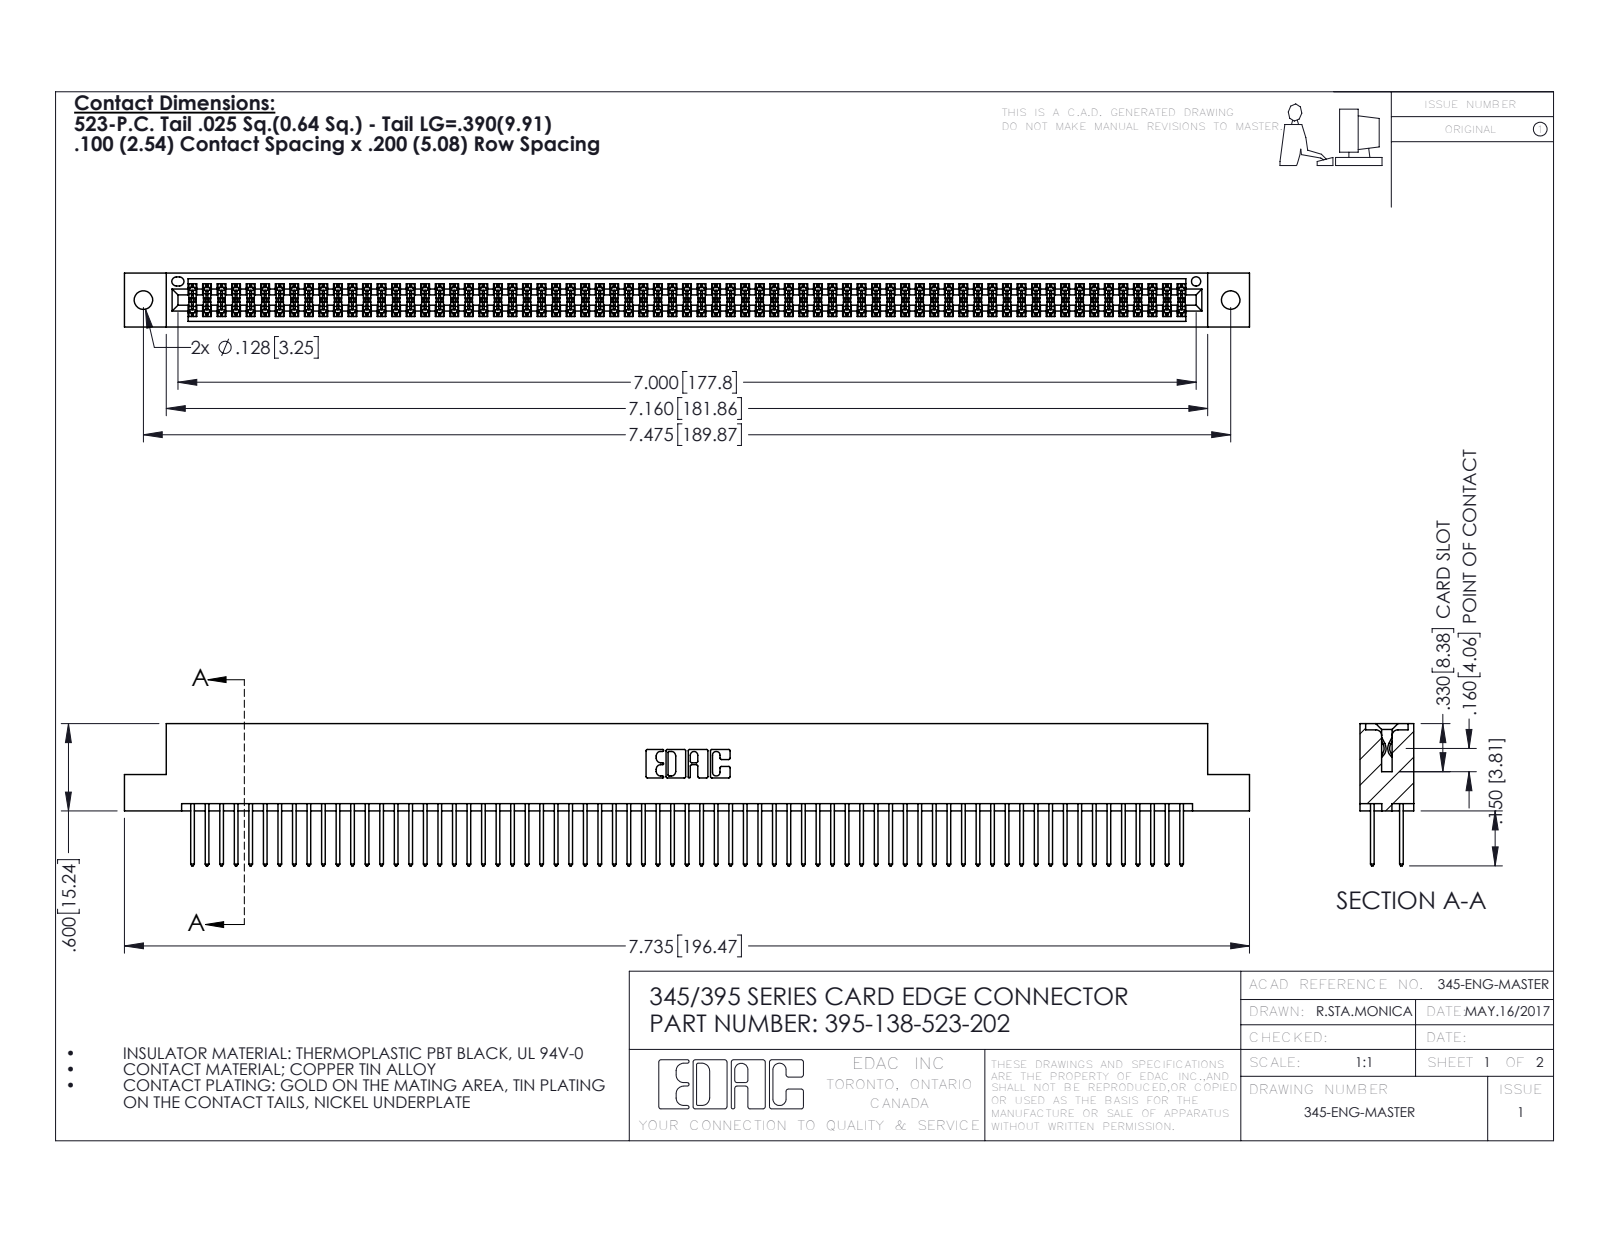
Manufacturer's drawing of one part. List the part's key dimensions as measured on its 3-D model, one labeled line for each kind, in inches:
Part name (STEP PRODUCT): 345 Part_Flush Mounting Lugs - 0.128 Dia; 345-292-001_345-293-123; 395-138-523-202
STEP written by: SolidWorks 2016 (CONFIG_CONTROL_DESIGN)
Units: inches
Bodies: 139 solids, 7026 faces (4634 planar, 2392 cylindrical, 0 other)
Overall size (bounding box): 7.735 × 0.977 × 0.37
Volume: 1.195 in³ · Surface area: 47.22 in²
Round holes (diameter × count): ⌀0.128 ×2, ⌀0.064 ×1
Partial cylindrical surfaces — rounded edges, fillets, slot ends (radius × count): R0.006 ×207, R0.01 ×138, R0.01 ×22, R0.007 ×6, R0.031 ×6, R0.026 ×3, R0.014 ×2, R0.019 ×2
Main face-to-face distances: 0.298, 0.072, 0.2, 0.098, 0.272, 0.025, 0.37, 0.225, 0.175, 0.149
Hole centre spacings: 0.27, 7.239, 7.475
